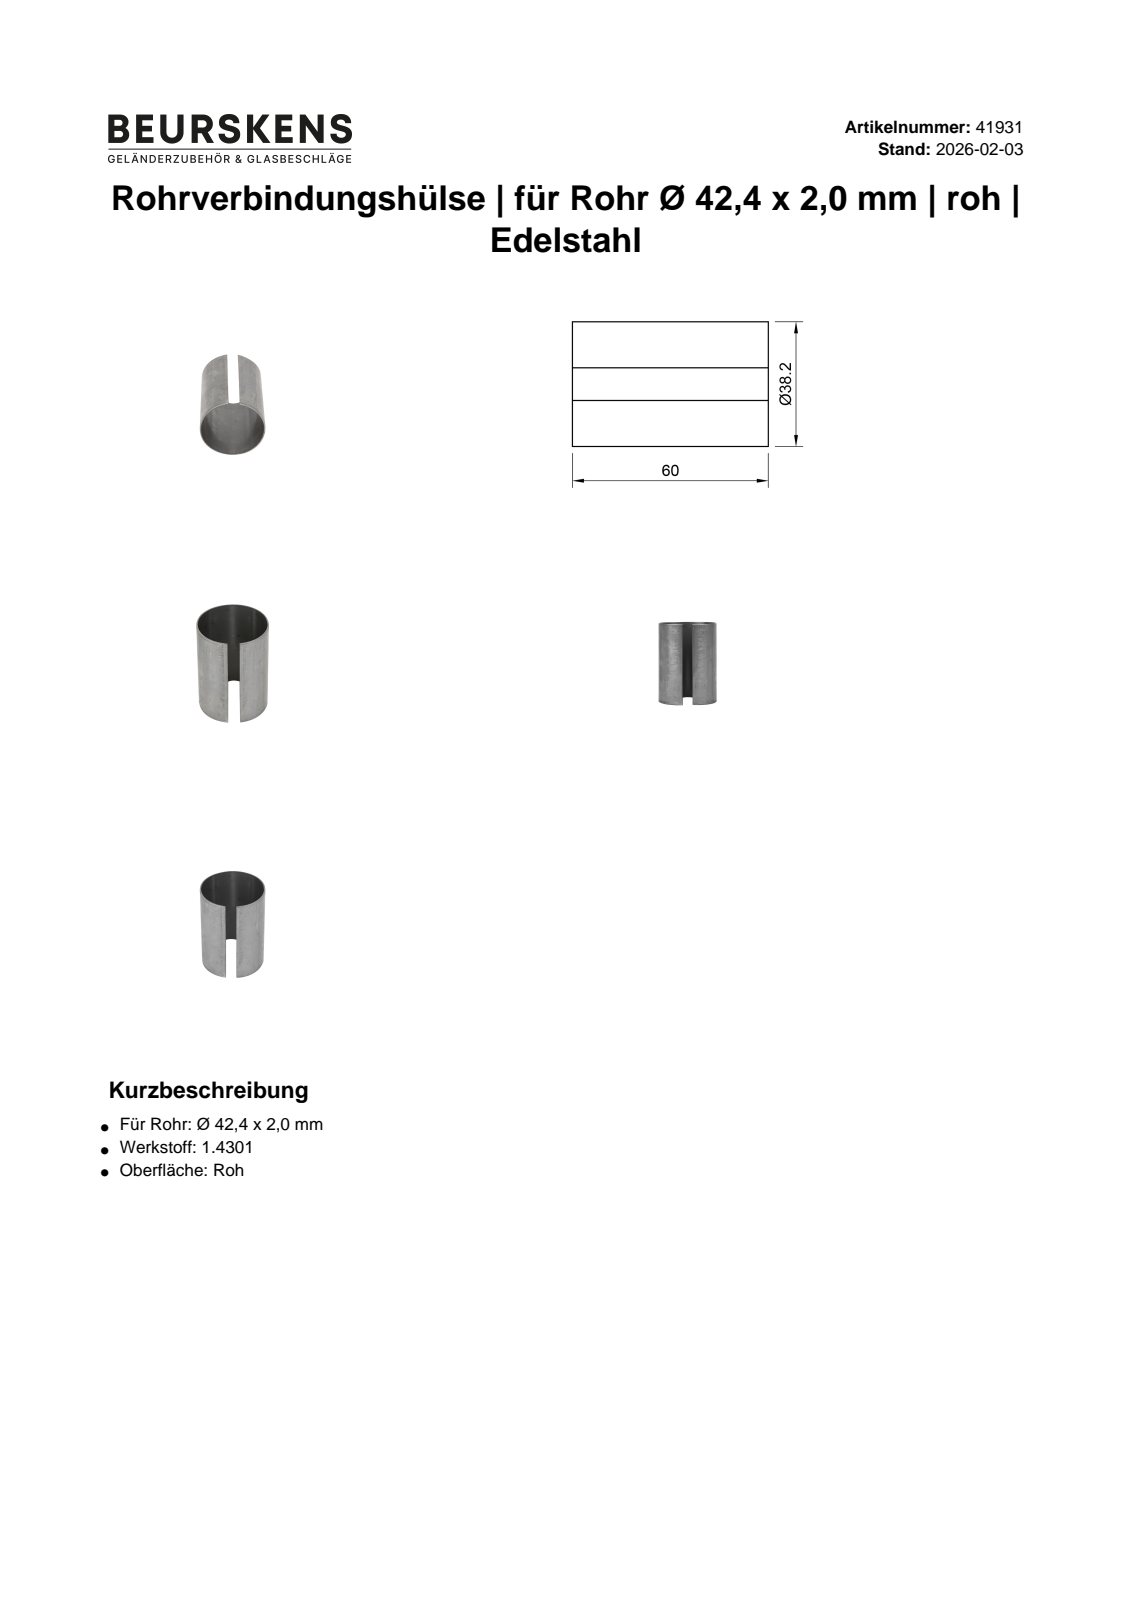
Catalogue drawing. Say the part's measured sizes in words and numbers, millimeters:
The part is named "41931". Its 3-D file was written by "Autodesk Inventor 2022 (AUTOMOTIVE_DESIGN)". It is 1 solid with 6 faces: 4 planar, 2 cylindrical and 0 other. Overall it measures 60 by 38.2 by 37.53 millimeters. Its volume is 3 250 cubic millimeters and its surface area 13 169 square millimeters. Round holes: 1 of diameter 37.2. Round bosses or shafts: 1 of diameter 38.2. The main face-to-face distances are 60, 10.
